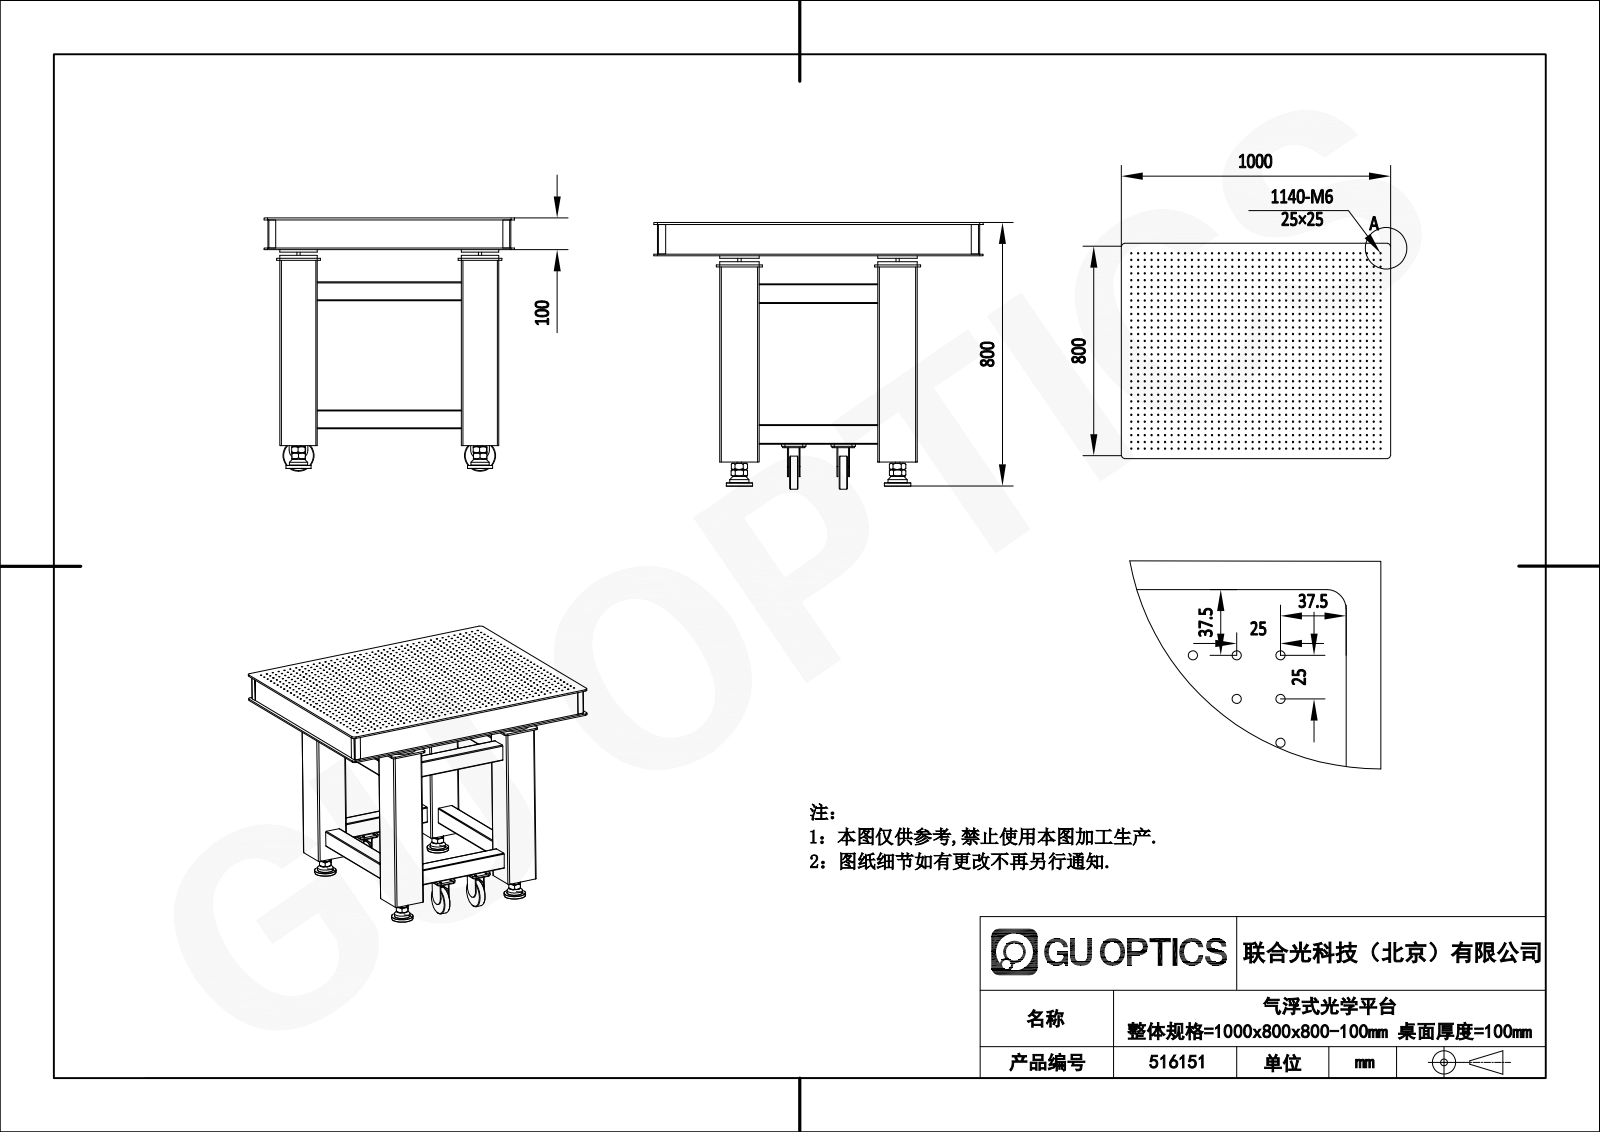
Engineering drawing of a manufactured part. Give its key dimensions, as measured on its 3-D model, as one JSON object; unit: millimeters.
{"part_name": "516151", "step_written_by": "SolidWorks 2020 (CONFIG_CONTROL_DESIGN)", "units": "millimeters", "bodies": {"solids": 62, "faces": 4461, "planar": 1629, "cylindrical": 2640, "other": 192}, "overall_size": [1000, 809, 800], "volume_mm3": 85660000, "surface_area_mm2": 8340000, "round_holes": [[5.3, 1140], [8.5, 16], [9, 16], [17.5, 4], [22, 4], [28, 4], [43, 4]], "round_bosses_or_shafts": [[120, 4], [80, 4], [58, 4], [14, 4], [10, 4], [100, 2]], "partial_cylinders_radius": [[1, 48], [10, 48], [3, 36], [5, 16], [7, 16], [2, 4], [11, 4], [30, 2]], "face_to_face_distances": [4, 116, 5, 480, 96, 101, 580, 2, 58, 112], "hole_center_spacings": [150, 580, 25, 45, 50, 78, 90.05, 147.74]}
